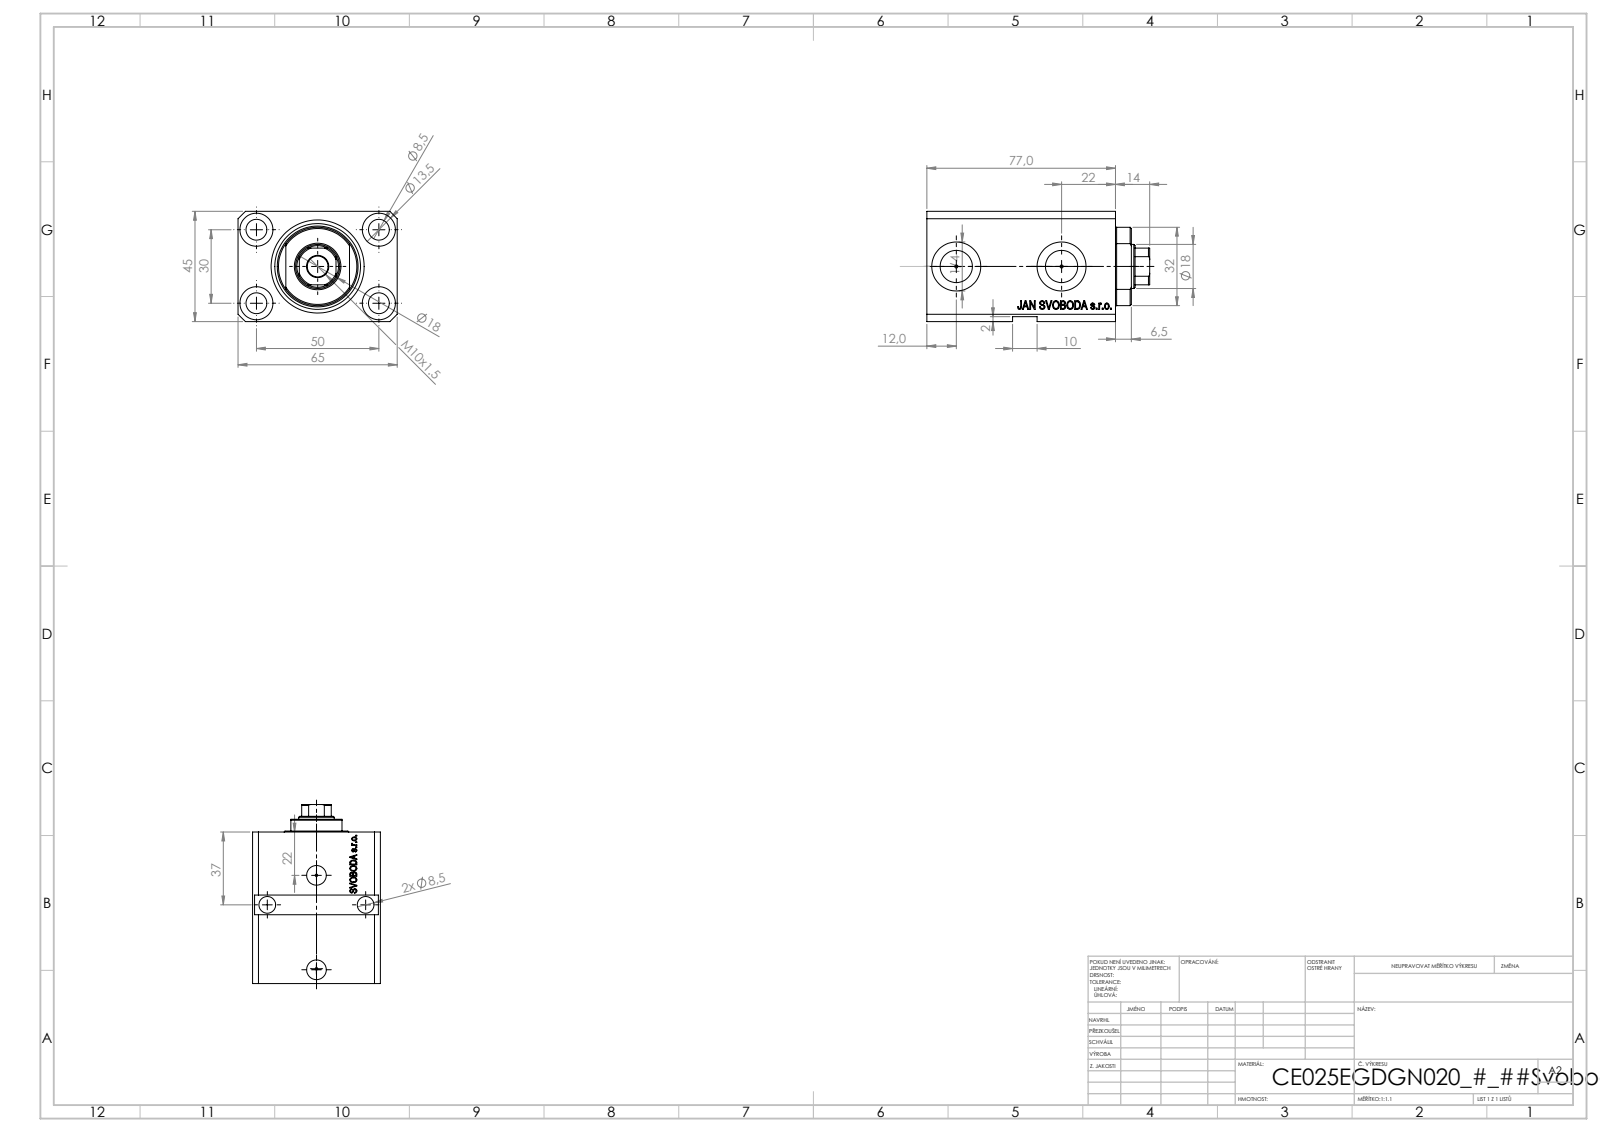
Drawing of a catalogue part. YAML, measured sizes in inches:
part_name: "V250CE_E_Body; V250CE_C_VCP; V250CE_VC_E"
step_written_by: "SolidWorks 2019 (CONFIG_CONTROL_DESIGN)"
units: inches
bodies: {solids: 3, faces: 913, planar: 439, cylindrical: 96, other: 378}
overall_size: [3.583, 2.559, 1.772]
volume: 11.48
surface_area: 82.76
round_holes:
  - {diameter: 0.335, count: 7}
  - {diameter: 0.049, count: 4}
  - {diameter: 0.531, count: 4}
  - {diameter: 0.394, count: 2}
  - {diameter: 0.518, count: 2}
  - {diameter: 0.787, count: 2}
  - {diameter: 0.709, count: 1}
  - {diameter: 0.984, count: 1}
  - {diameter: 1.496, count: 1}
partial_cylinders:
  - {radius: 0.335, count: 1}
  - {radius: 0.63, count: 1}
face_to_face_distances: [1.772, 2.559, 2.48, 0.551, 3.031, 0.272, 2.209, 2.76, 1.693, 2.555]
hole_center_spacings: [1.148, 1.969, 1.181, 1.613, 1.63, 2.296, 0.021, 1.693]
